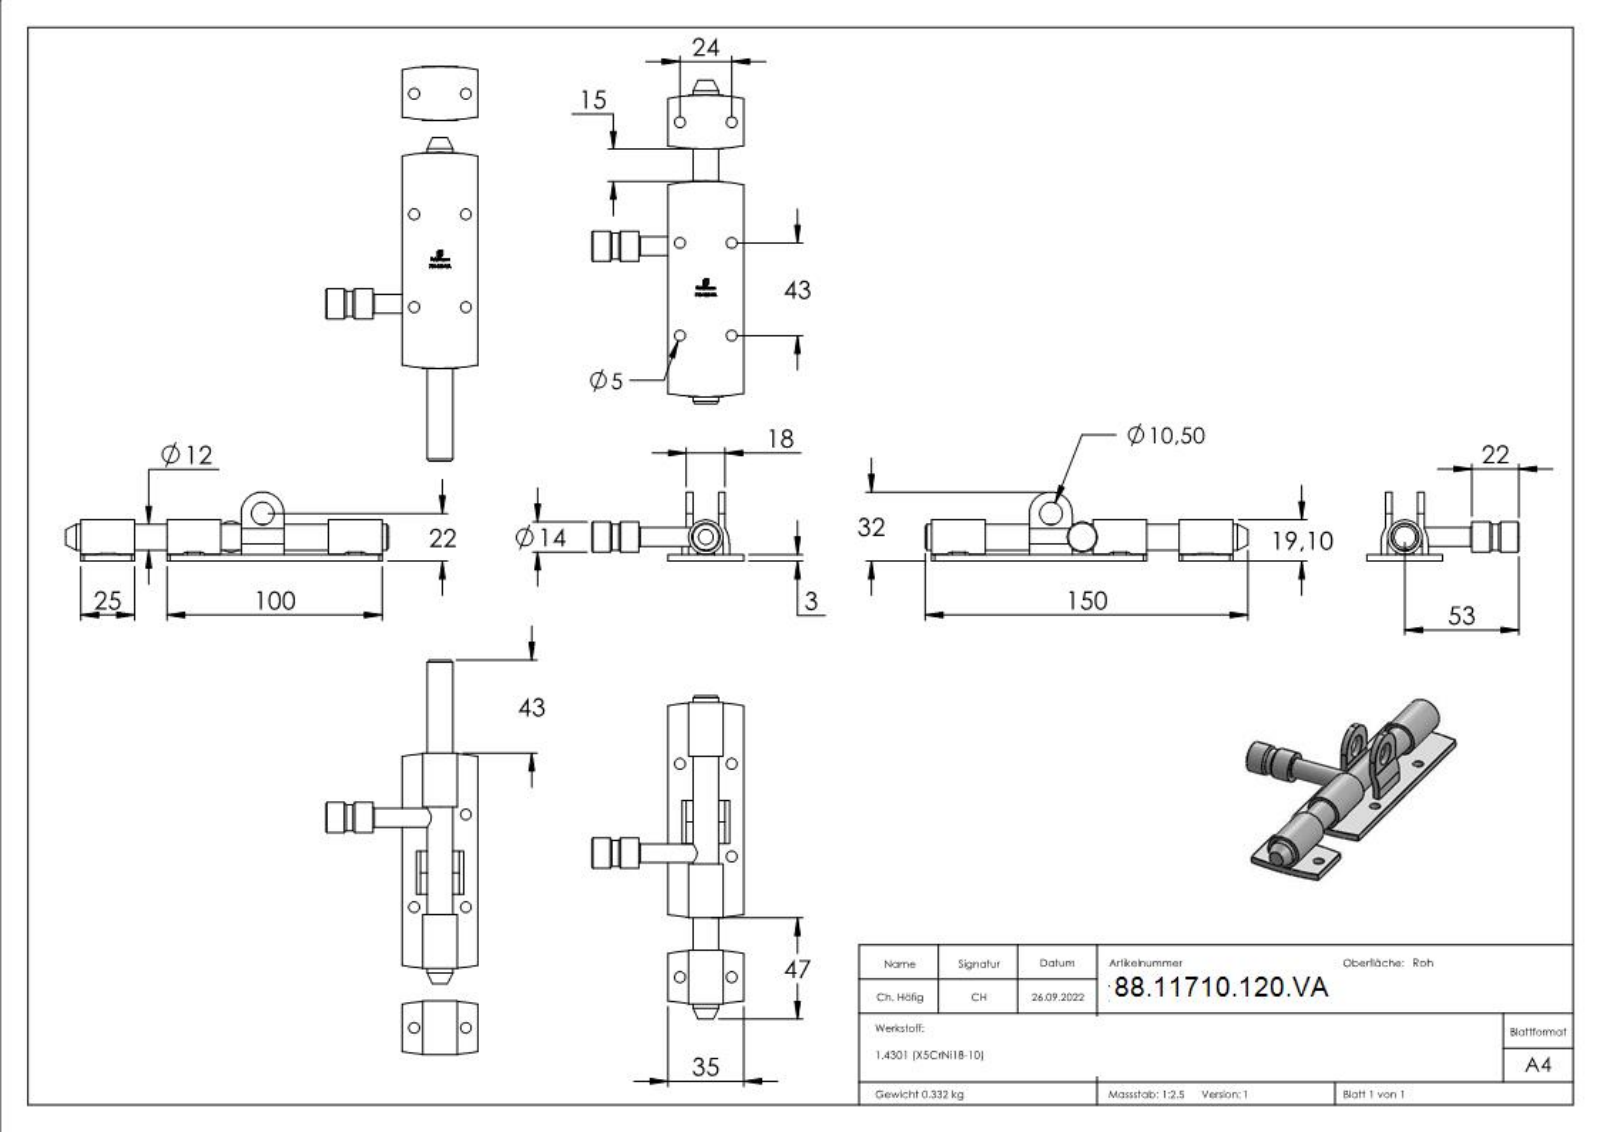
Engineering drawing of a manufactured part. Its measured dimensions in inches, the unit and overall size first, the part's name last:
Units: inches
Overall size (bounding box): 5.906 × 2.776 × 1.26
Round holes (diameter × count): ⌀0.197 ×6, ⌀0.413 ×1, ⌀0.512 ×1
Round bosses / shafts (diameter × count): ⌀0.472 ×2, ⌀0.63 ×1, ⌀0.551 ×1, ⌀0.346 ×1
Partial cylindrical surfaces — rounded edges, fillets, slot ends (radius × count): R0.079 ×10, R4.048 ×4, R0.394 ×3, R0.404 ×2, R0.522 ×2
Main face-to-face distances: 0.118, 0.591, 0.079, 0.335, 1.043, 0.669, 0.787, 1.378, 0.453, 0.925
Hole centre spacings: 0.945, 1.693, 1.939, 2.205, 2.399, 3.898, 4.011
Volume: 2.563 in³ · Surface area: 41.29 in²
Bodies: 3 solids, 336 faces (189 planar, 43 cylindrical, 104 other)
Part name (STEP PRODUCT): 710-XX0 Teil3_710-120-VA Teil3; 710-120-VA; 710-XX0 Teil2_710-120-VA Teil2; 710-XX0 Teil1_710-120-VA Teil1
STEP written by: SolidWorks 2018 (CONFIG_CONTROL_DESIGN)
